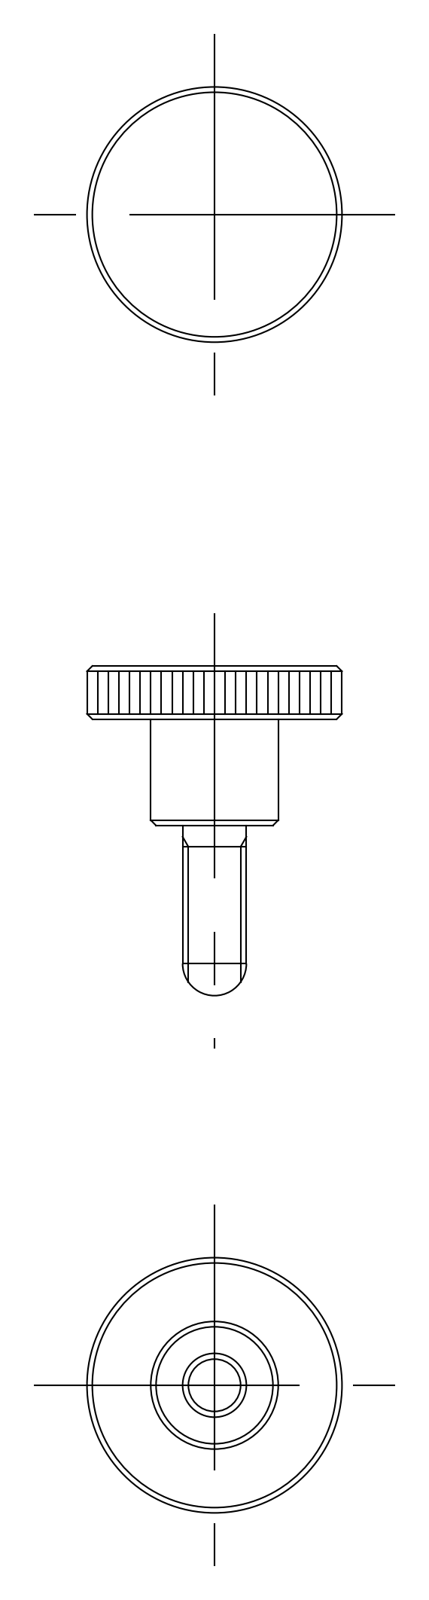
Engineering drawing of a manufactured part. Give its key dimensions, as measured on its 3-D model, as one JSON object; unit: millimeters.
{"part_name": "knob", "step_written_by": "CADfix (AUTOMOTIVE_DESIGN)", "units": "millimeters", "bodies": {"solids": 1, "faces": 16, "planar": 0, "cylindrical": 0, "other": 16}, "overall_size": [31, 24, 24], "volume_mm3": 3800, "surface_area_mm2": 1876}
